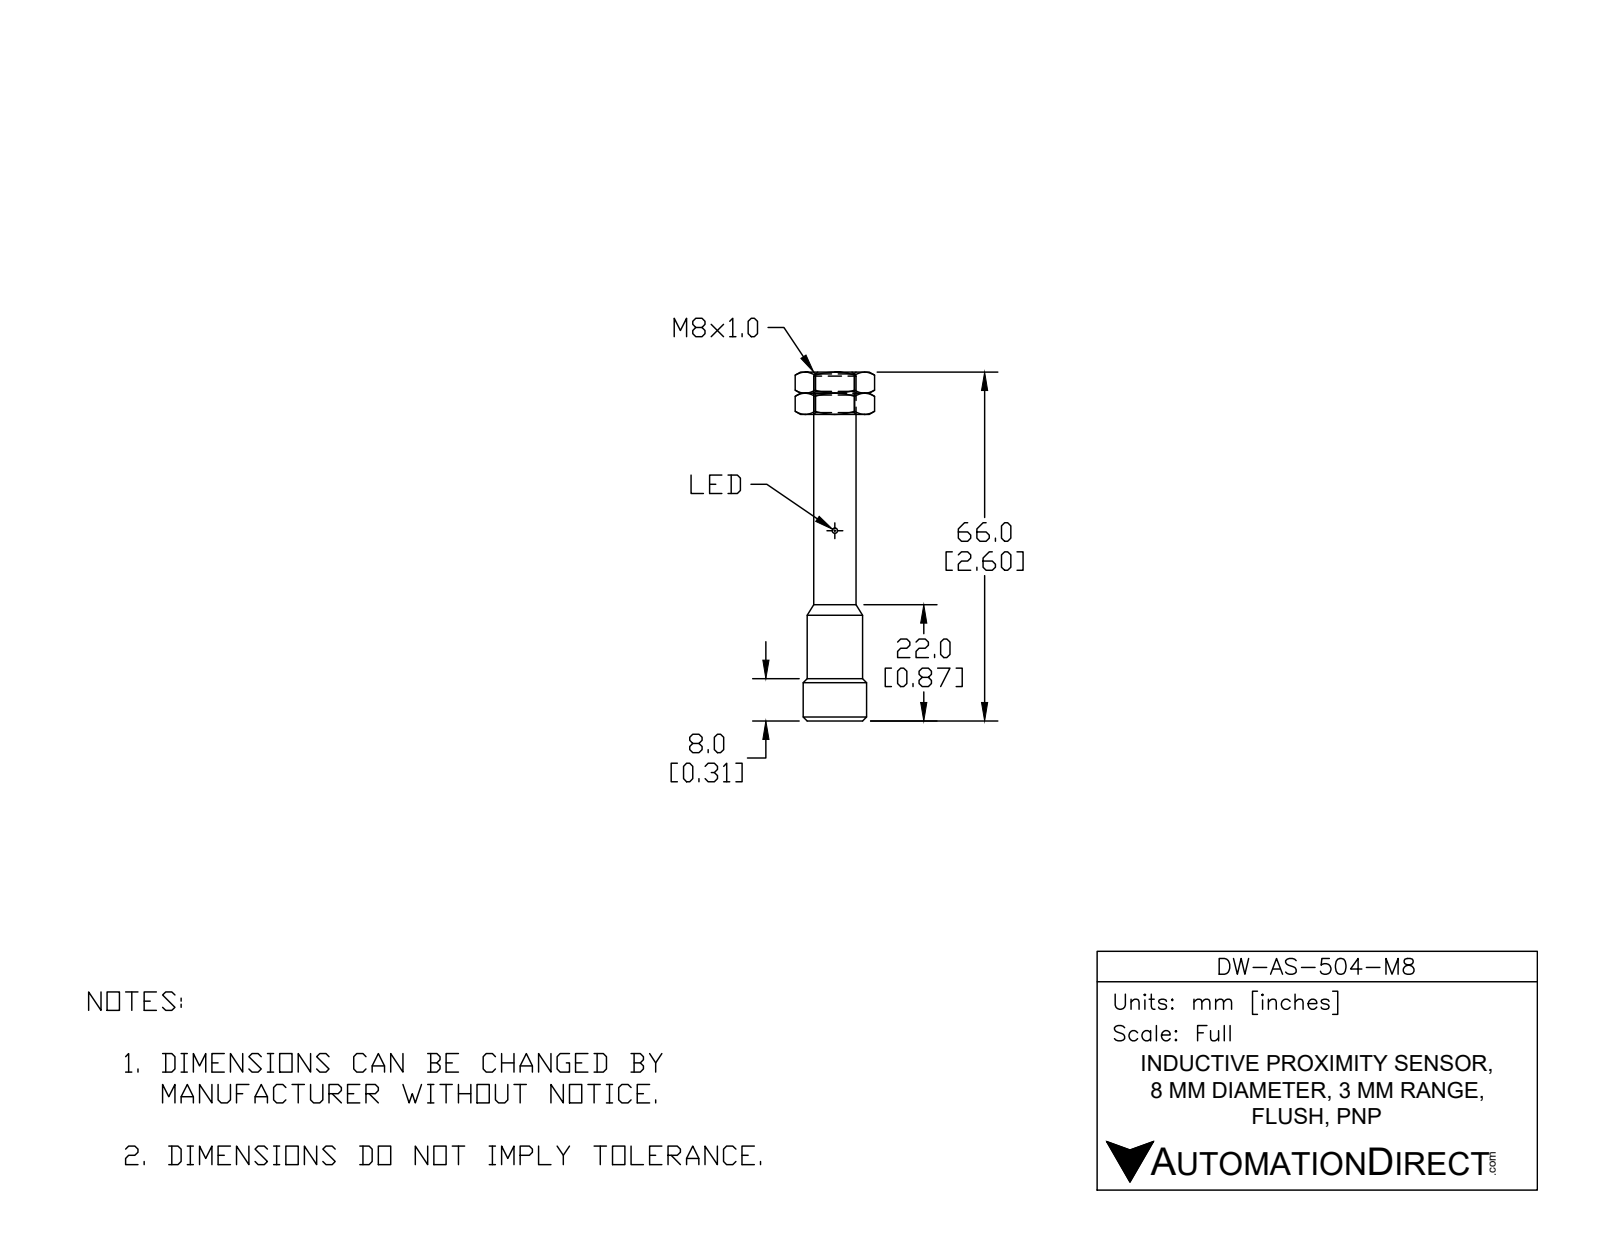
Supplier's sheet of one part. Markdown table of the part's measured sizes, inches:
| quantity | value |
| --- | --- |
| part name | DW-AS-504-M8 |
| STEP written by | SolidWorks 2017 (AUTOMOTIVE_DESIGN) |
| units | inches |
| bodies | 1 solid, 35 faces (10 planar, 17 cylindrical, 8 other) |
| overall size | 2.598 × 0.472 × 0.472 |
| volume | 0.23 in³ |
| surface area | 3.709 in² |
| round holes (diameter × count) | 0.12 × 2 |
| round bosses / shafts (diameter × count) | 0.039 × 4, 0.472 × 1, 0.415 × 1, 0.335 × 1, 0.315 × 1 |
| main face-to-face distances | 2.256, 2.598, 0.343, 1.811, 0.445, 0.787, 1.593, 0.218, 0.663, 1.005 |
